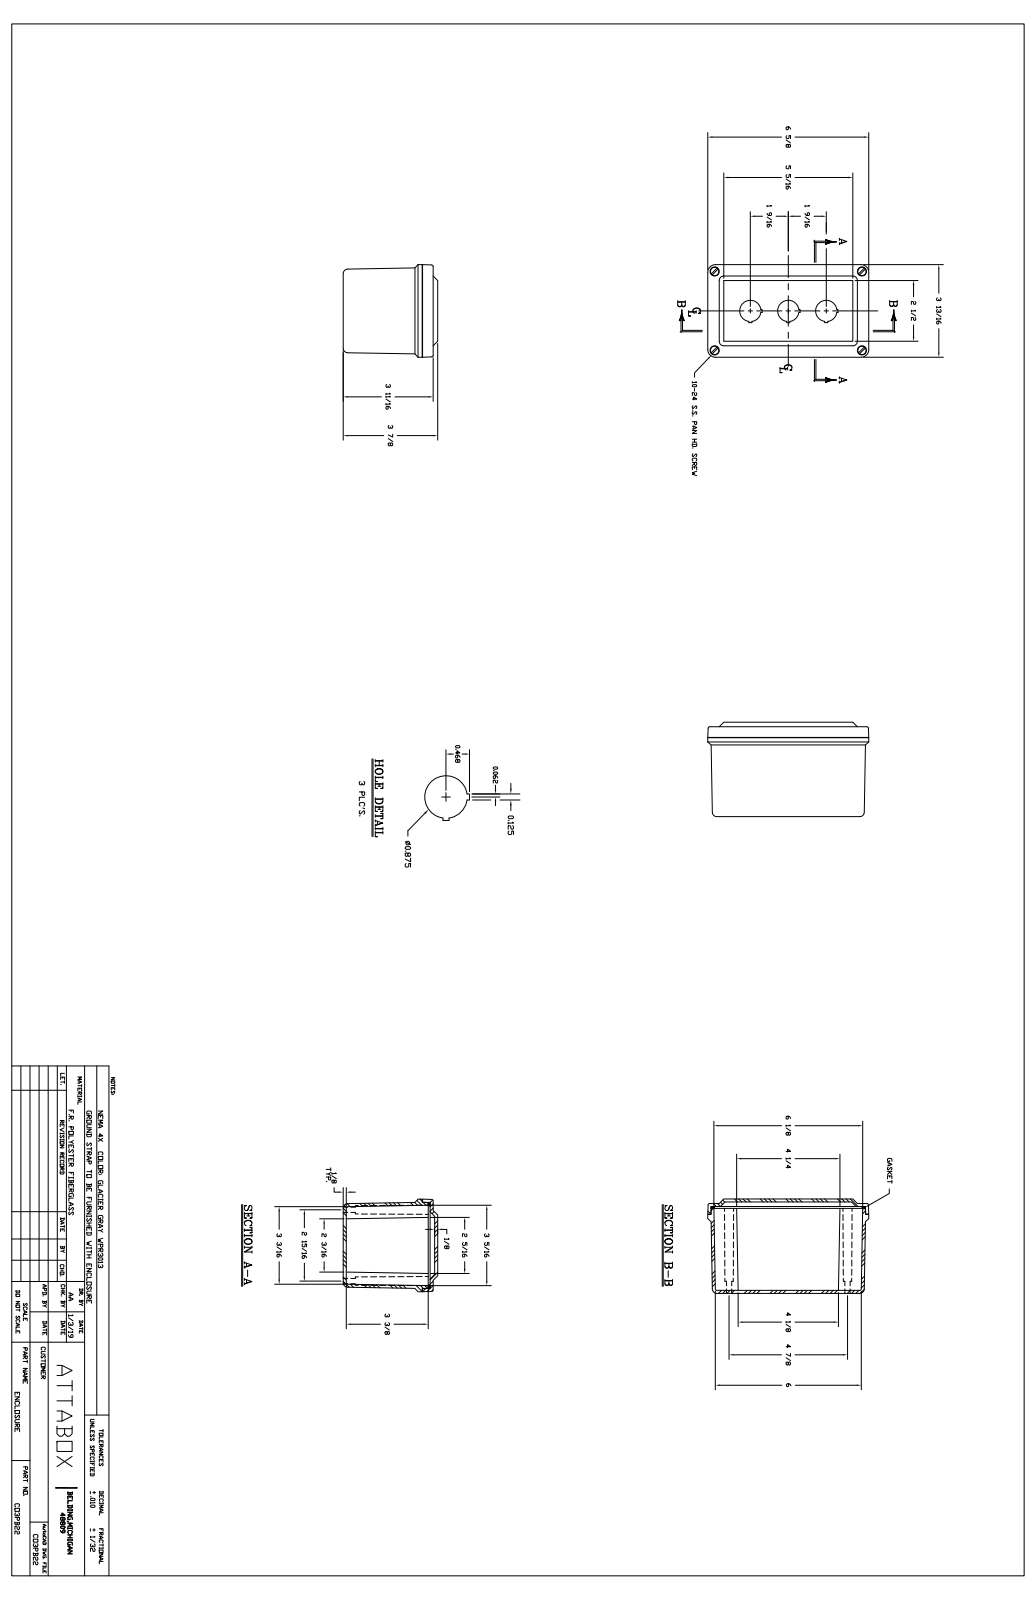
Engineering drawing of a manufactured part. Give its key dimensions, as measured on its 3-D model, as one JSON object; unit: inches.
{"part_name": "CO3PB22", "step_written_by": "SolidWorks 2018 (AUTOMOTIVE_DESIGN)", "units": "inches", "bodies": {"solids": 1, "faces": 398, "planar": 196, "cylindrical": 110, "other": 92}, "overall_size": [6.625, 3.875, 3.813], "volume_in3": 20.27, "surface_area_in2": 247.8, "round_holes": [[0.219, 8], [0.19, 4], [0.375, 4], [0.875, 2]], "round_bosses_or_shafts": [[0.371, 4], [0.218, 4], [0.177, 4]], "partial_cylinders_radius": [[0.031, 20], [0.012, 16], [0.313, 8], [0.176, 4], [0.188, 4], [0.22, 4], [0.325, 4], [0.062, 2]], "face_to_face_distances": [0.135, 0.125, 3.75, 0.187, 3.563, 3.875, 3.625, 0.5, 0.635, 0.063], "hole_center_spacings": [0.614, 5.471, 6.283, 2.846, 3.15, 3.439, 6.062, 1.71]}
